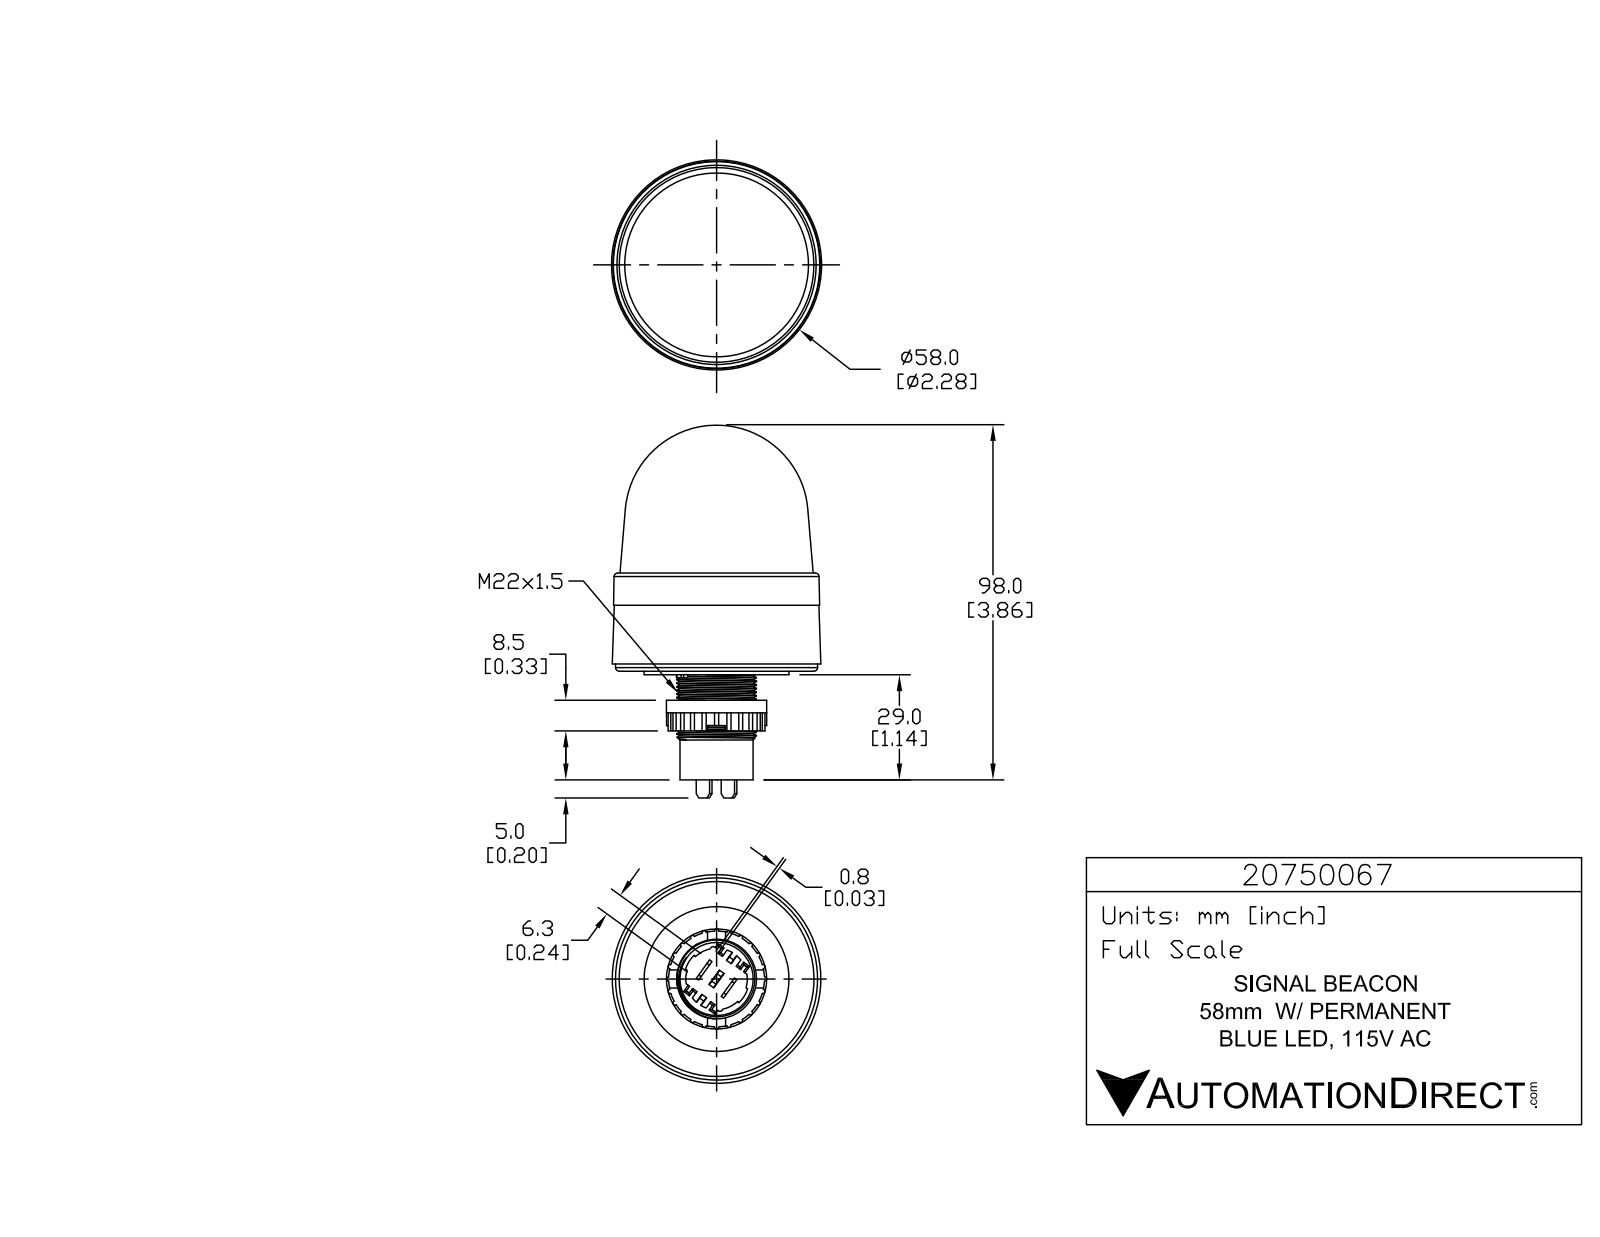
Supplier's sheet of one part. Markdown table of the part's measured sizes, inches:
| quantity | value |
| --- | --- |
| part name | 20750067 |
| STEP written by | SolidWorks 2015 (AUTOMOTIVE_DESIGN) |
| units | inches |
| bodies | 1 solid, 266 faces (119 planar, 120 cylindrical, 27 other) |
| overall size | 4.051 × 2.269 × 2.269 |
| volume | 9.016 in³ |
| surface area | 31.05 in² |
| round holes (diameter × count) | 0.906 × 1 |
| round bosses / shafts (diameter × count) | 2.197 × 1, 1.575 × 1, 1.091 × 1, 0.866 × 1, 0.795 × 1 |
| partial cylindrical surfaces (radius × count) | 0.023 × 24, 0.02 × 2, 0.335 × 1, 0.354 × 1, 0.522 × 1 |
| main face-to-face distances | 0.039, 0.276, 0.118, 1.142, 0.335, 0.315, 1.063, 0.748, 1.024, 0.728 |
